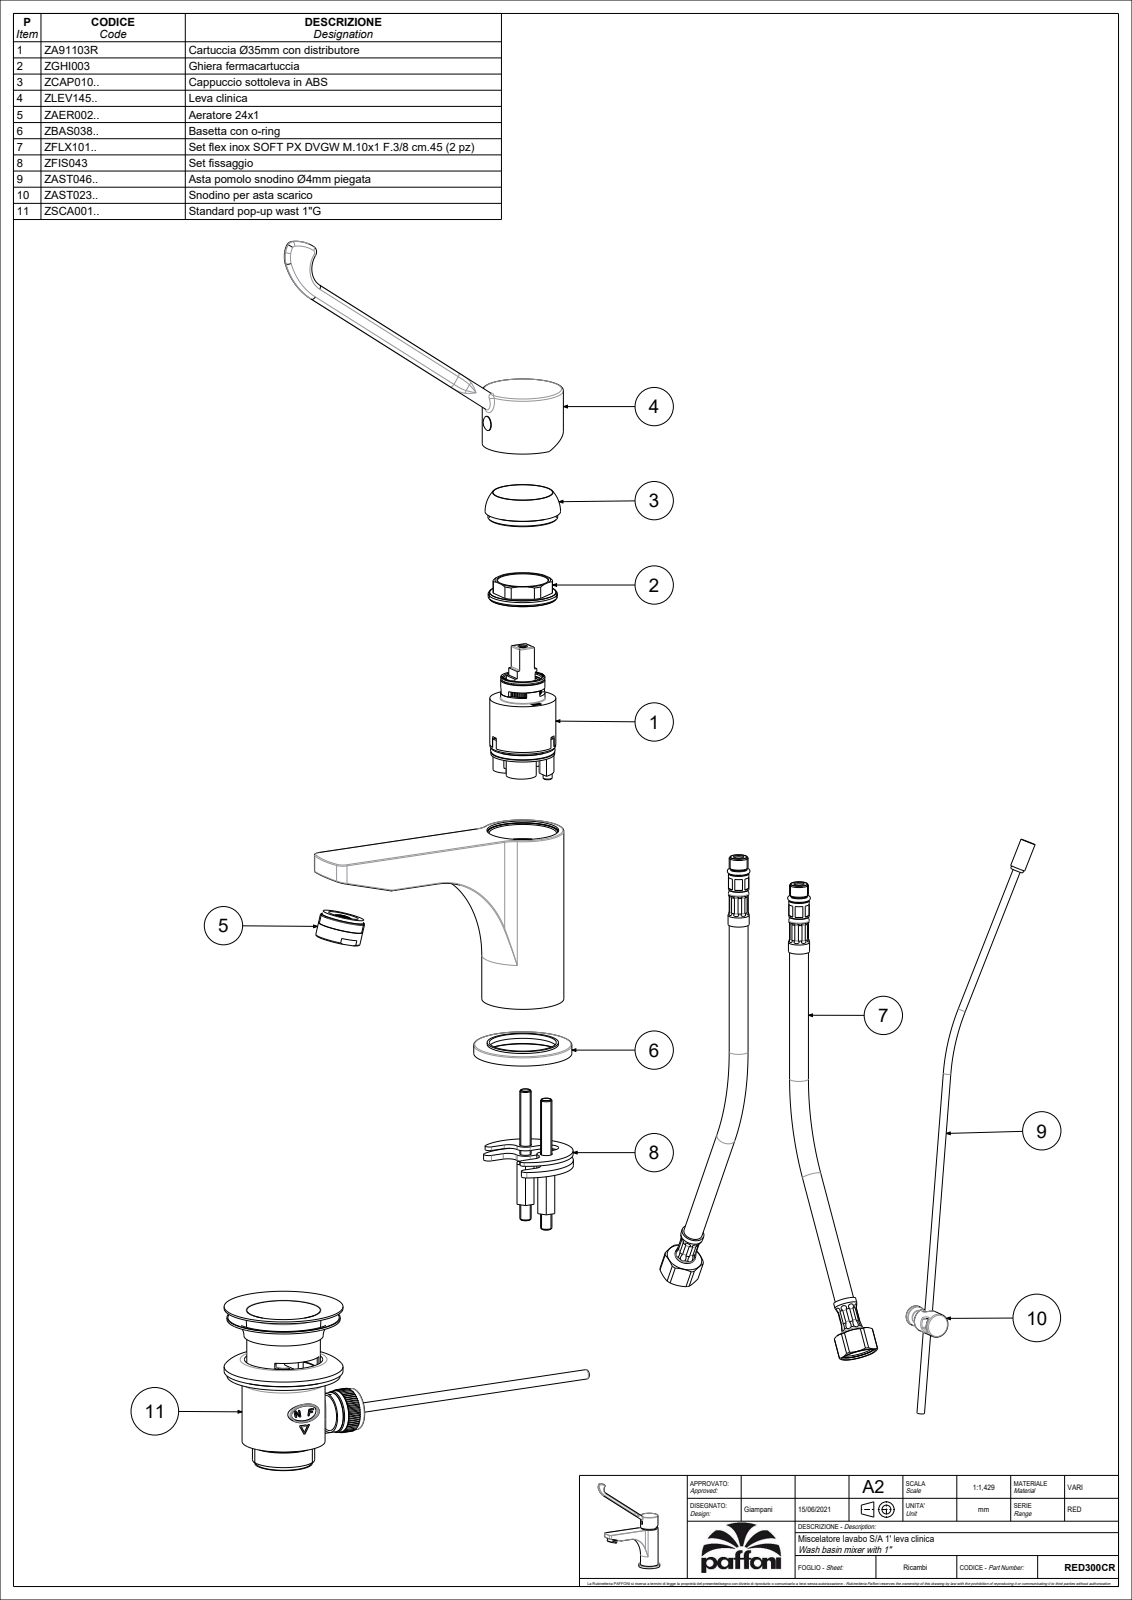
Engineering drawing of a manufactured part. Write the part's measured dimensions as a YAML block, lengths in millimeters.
part_name: "RED300CR"
step_written_by: "CREO PARAMETRIC BY PTC INC, 2020044 (CONFIG_CONTROL_DESIGN)"
units: millimeters
bodies: {solids: 6, faces: 3105, planar: 2171, cylindrical: 539, other: 395}
overall_size: [229.58, 183.37, 52]
volume: 147406
surface_area: 97815
round_holes:
  - {diameter: 9, count: 5}
  - {diameter: 5, count: 4}
  - {diameter: 4.5, count: 3}
  - {diameter: 12, count: 3}
  - {diameter: 4, count: 2}
  - {diameter: 5.5, count: 2}
  - {diameter: 6, count: 2}
  - {diameter: 6.5, count: 2}
  - {diameter: 8, count: 2}
  - {diameter: 3, count: 1}
  - {diameter: 3.3, count: 1}
  - {diameter: 3.5, count: 1}
round_bosses_or_shafts:
  - {diameter: 11.2, count: 2}
  - {diameter: 10.8, count: 2}
  - {diameter: 10, count: 2}
  - {diameter: 8.2, count: 2}
  - {diameter: 6, count: 2}
  - {diameter: 4.8, count: 2}
  - {diameter: 52, count: 1}
  - {diameter: 44.5, count: 1}
partial_cylinders:
  - {radius: 0.5, count: 88}
  - {radius: 1, count: 26}
  - {radius: 1.26, count: 14}
  - {radius: 2.05, count: 14}
  - {radius: 0.15, count: 11}
  - {radius: 0.3, count: 9}
  - {radius: 2, count: 4}
  - {radius: 7, count: 4}
face_to_face_distances: [3.5, 27.5, 31, 4.5, 13.25, 14.25, 9.75, 17.75, 15.5, 24]
hole_center_spacings: [13.6, 0.71, 2.83, 8.51, 8.6, 9.66, 9.85, 11.18]
